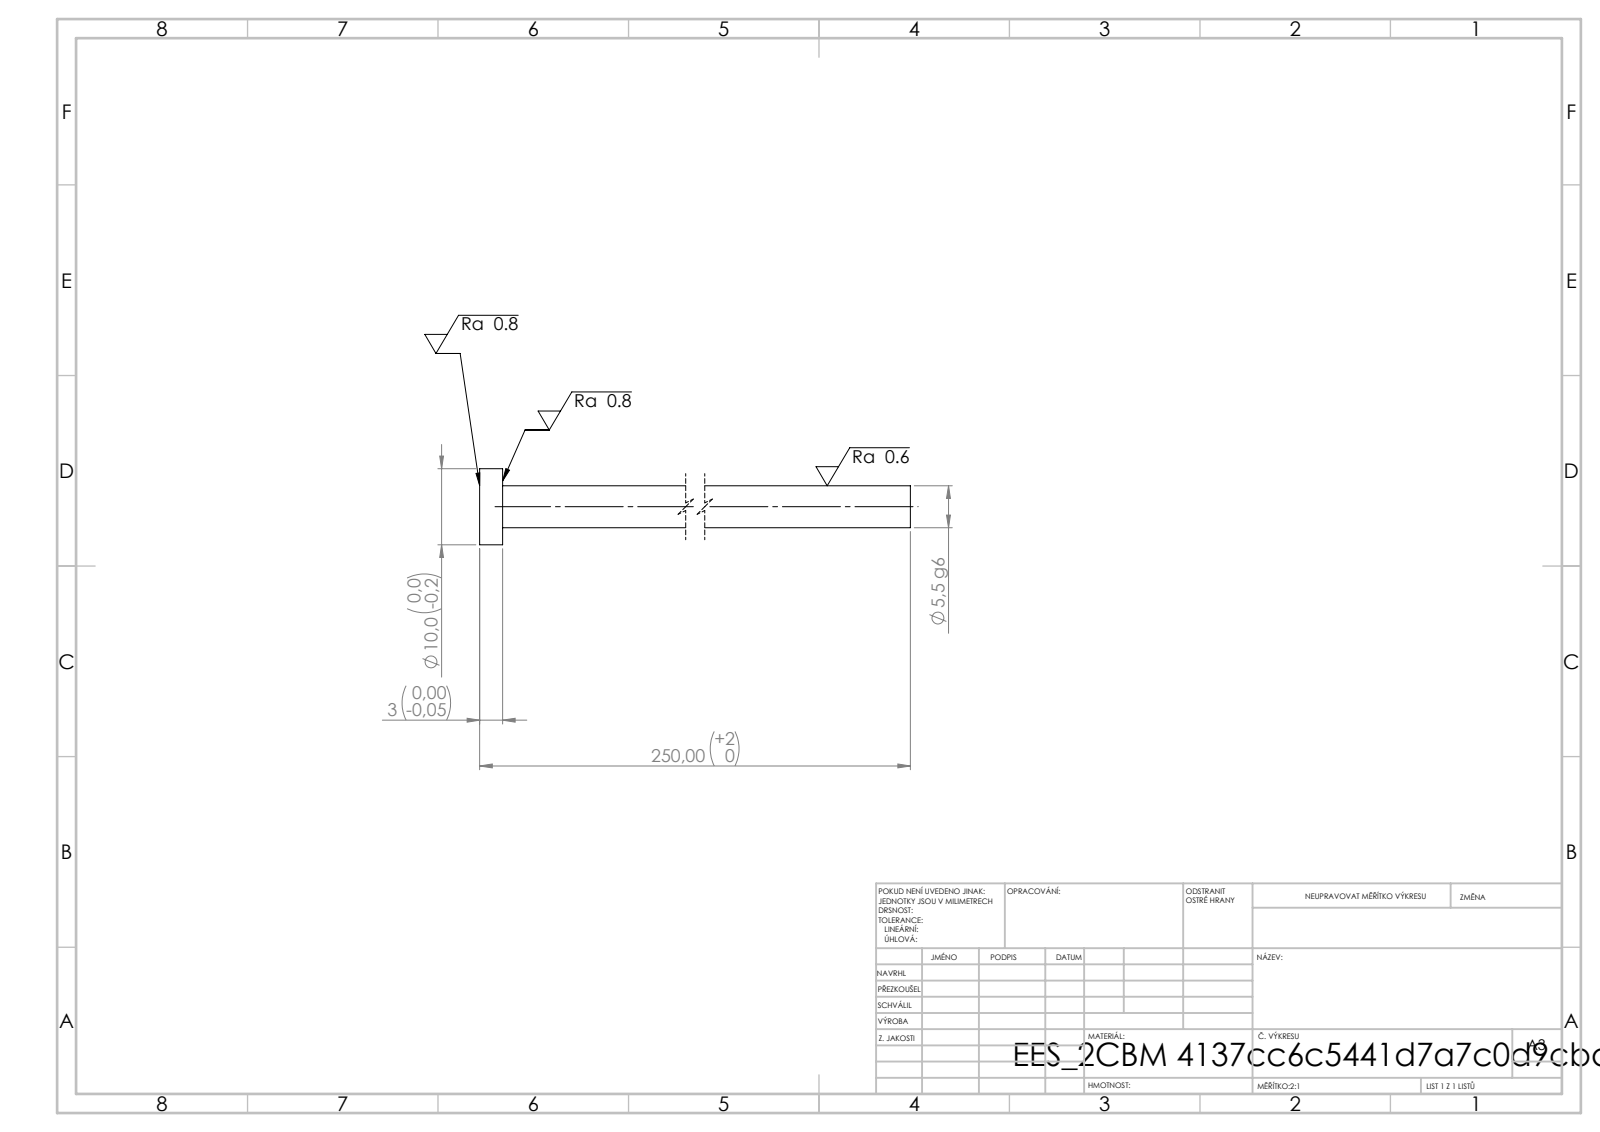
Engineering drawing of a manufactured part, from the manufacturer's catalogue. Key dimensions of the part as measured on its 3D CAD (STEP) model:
STEP written by: SolidWorks 2019 (CONFIG_CONTROL_DESIGN)
Units: millimetres
Bodies: 1 solid, 7 faces (3 planar, 4 cylindrical, 0 other)
Overall size (bounding box): 250 × 10 × 10
Volume: 6 104 mm³ · Surface area: 4 519 mm²
Round bosses / shafts (diameter × count): ⌀10 ×1, ⌀5.5 ×1
Main face-to-face distances: 3, 250, 247
